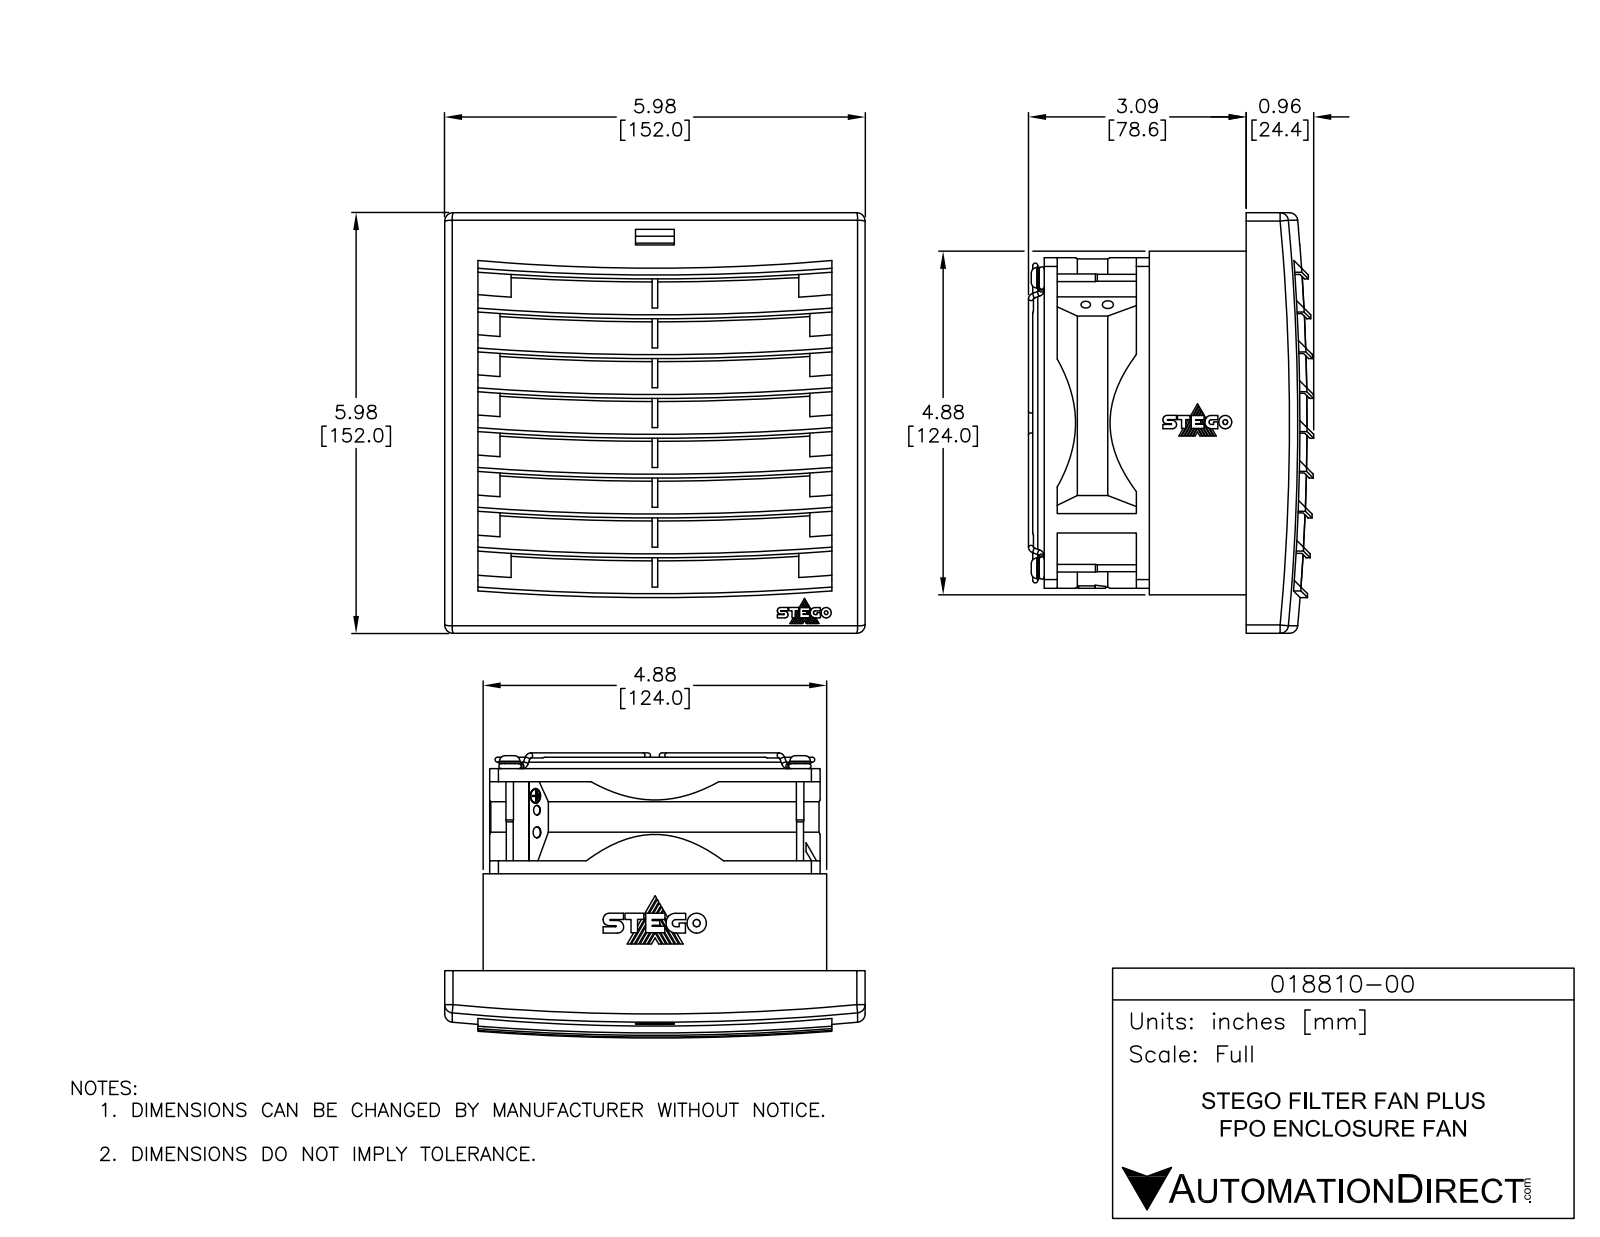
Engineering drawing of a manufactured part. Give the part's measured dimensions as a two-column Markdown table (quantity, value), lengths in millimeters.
| quantity | value |
| --- | --- |
| part name | 018810-00 |
| STEP written by | SolidWorks 2018 (AUTOMOTIVE_DESIGN) |
| units | millimeters |
| bodies | 1 solid, 544 faces (329 planar, 207 cylindrical, 8 other) |
| overall size | 152 × 152 × 104 |
| volume | 537 000 mm³ |
| surface area | 231 900 mm² |
| round holes (diameter × count) | 6.5 × 4, 24.9 × 1, 42.2 × 1, 59.4 × 1, 76.7 × 1, 82.6 × 1, 96 × 1, 105.4 × 1 |
| round bosses / shafts (diameter × count) | 110.4 × 1, 88.6 × 1, 80.7 × 1, 68.9 × 1, 63.4 × 1, 46.2 × 1, 33.6 × 1, 28.9 × 1 |
| partial cylindrical surfaces (radius × count) | 349.4 × 16, 47 × 5, 3 × 4, 3.6 × 4, 13.2 × 1, 21.6 × 1, 24.6 × 1, 31.4 × 1 |
| main face-to-face distances | 1.5, 10.8, 3.1, 120.9, 21.6, 2, 3.4, 6.8, 12.3, 9.3 |
| hole center spacings | 76.4, 108, 152.7 |
